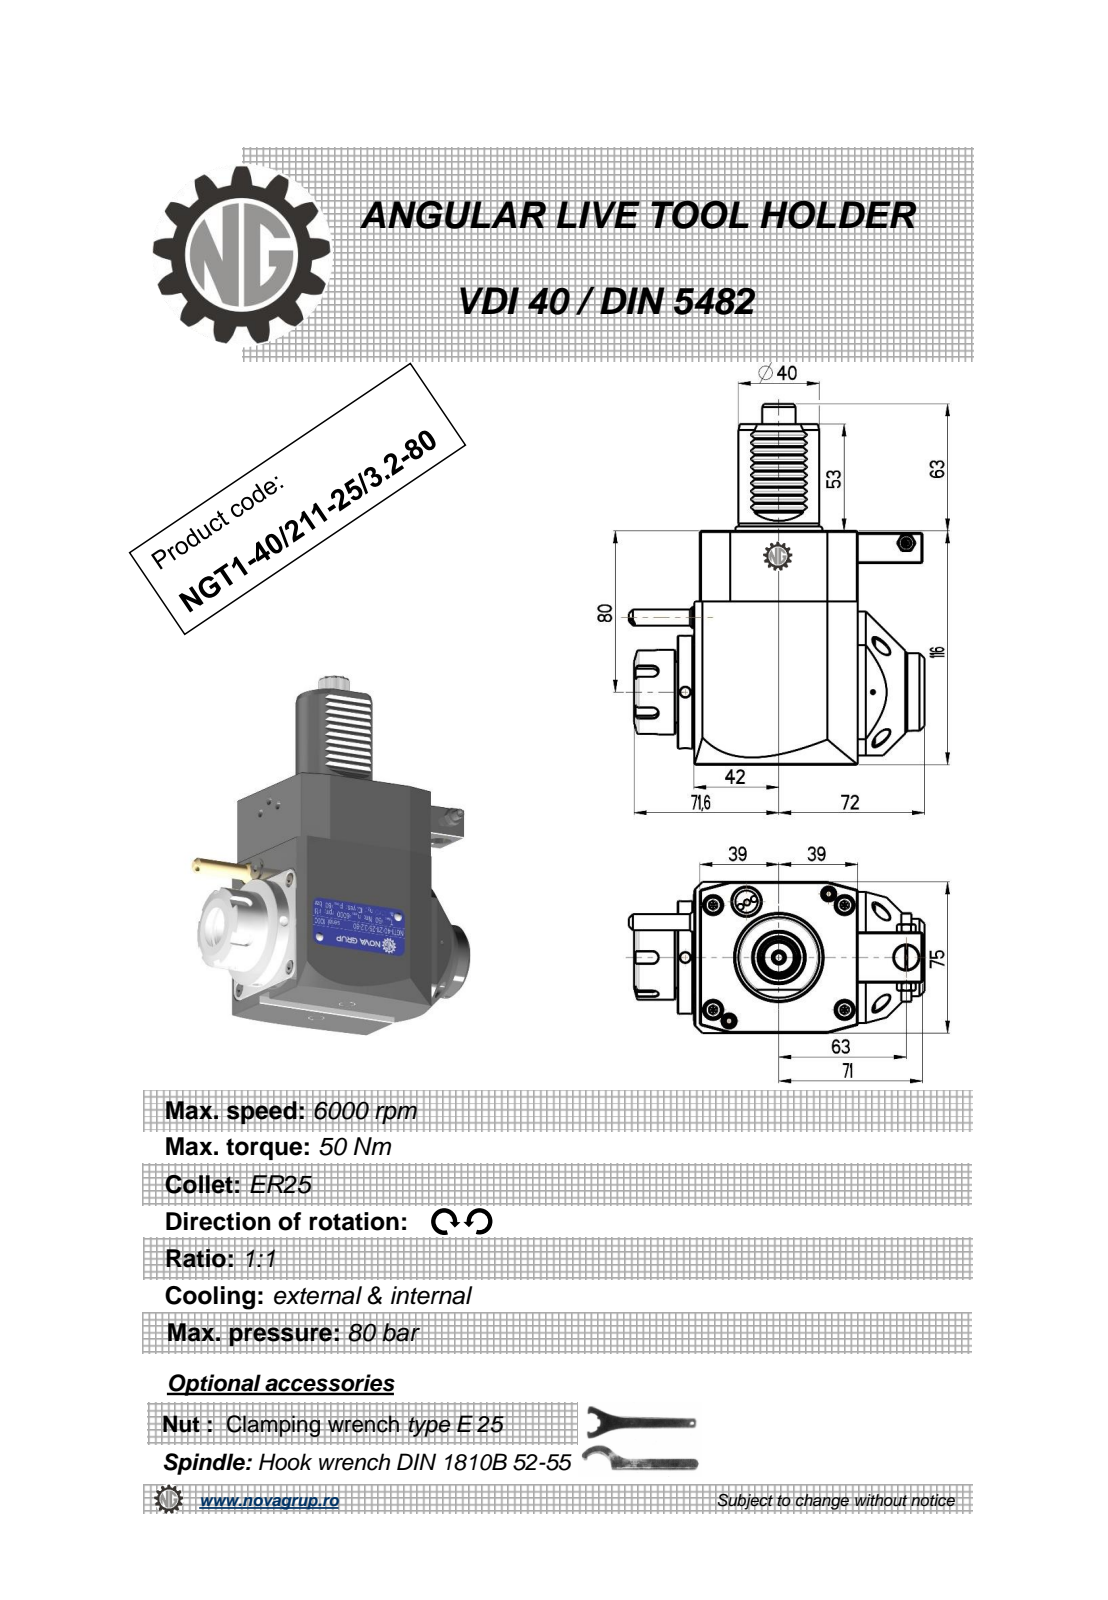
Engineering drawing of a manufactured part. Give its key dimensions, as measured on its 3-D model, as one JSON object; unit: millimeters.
{"part_name": "NGT1_40_211_25_3_2_80", "step_written_by": "PRO/ENGINEER BY PARAMETRIC TECHNOLOGY CORPORATION, 2010280 (CONFIG_CONTROL_DESIGN)", "units": "millimeters", "bodies": {"solids": 1, "faces": 473, "planar": 183, "cylindrical": 124, "other": 166}, "overall_size": [179, 146.14, 75], "volume_mm3": 884448, "surface_area_mm2": 71283, "round_holes": [[5, 3], [4.2, 2], [3, 1], [5.3, 1], [9.5, 1], [12, 1], [20.3, 1]], "round_bosses_or_shafts": [[56, 1], [43, 1], [42, 1], [40, 1], [38.5, 1], [33, 1], [11.2, 1], [8.96, 1]], "partial_cylinders_radius": [[3.03, 18], [0.26, 12], [0.3, 10], [0.22, 6], [3, 5], [0.5, 1], [6.75, 1], [8.25, 1]], "face_to_face_distances": [75, 116, 81, 78, 3, 11, 8, 111, 2.8, 80.8], "hole_center_spacings": [39.58, 40.93, 46.25, 63, 72.5, 109.25, 131.95]}
